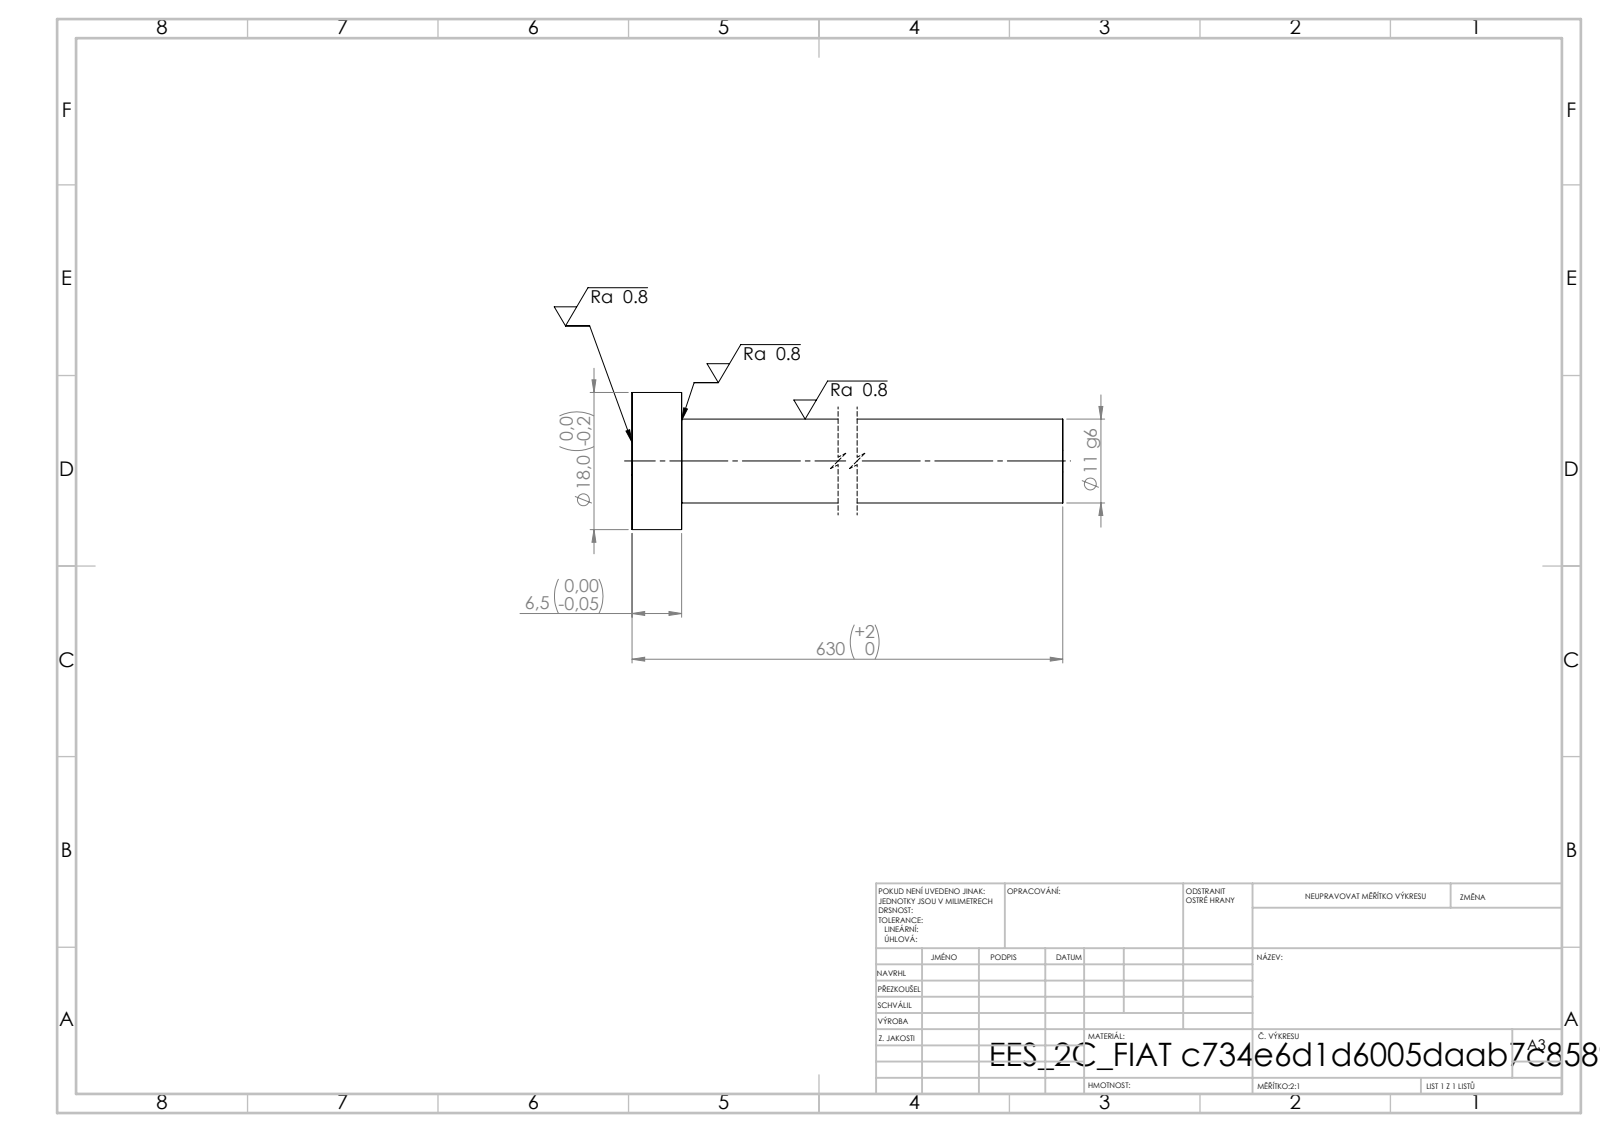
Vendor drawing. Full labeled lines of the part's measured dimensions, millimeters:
STEP written by: SolidWorks 2019 (CONFIG_CONTROL_DESIGN)
Units: millimetres
Bodies: 1 solid, 7 faces (3 planar, 4 cylindrical, 0 other)
Overall size (bounding box): 630 × 18 × 18
Volume: 60 907 mm³ · Surface area: 22 423 mm²
Round bosses / shafts (diameter × count): ⌀18 ×1, ⌀11 ×1
Main face-to-face distances: 6.5, 630, 623.5
